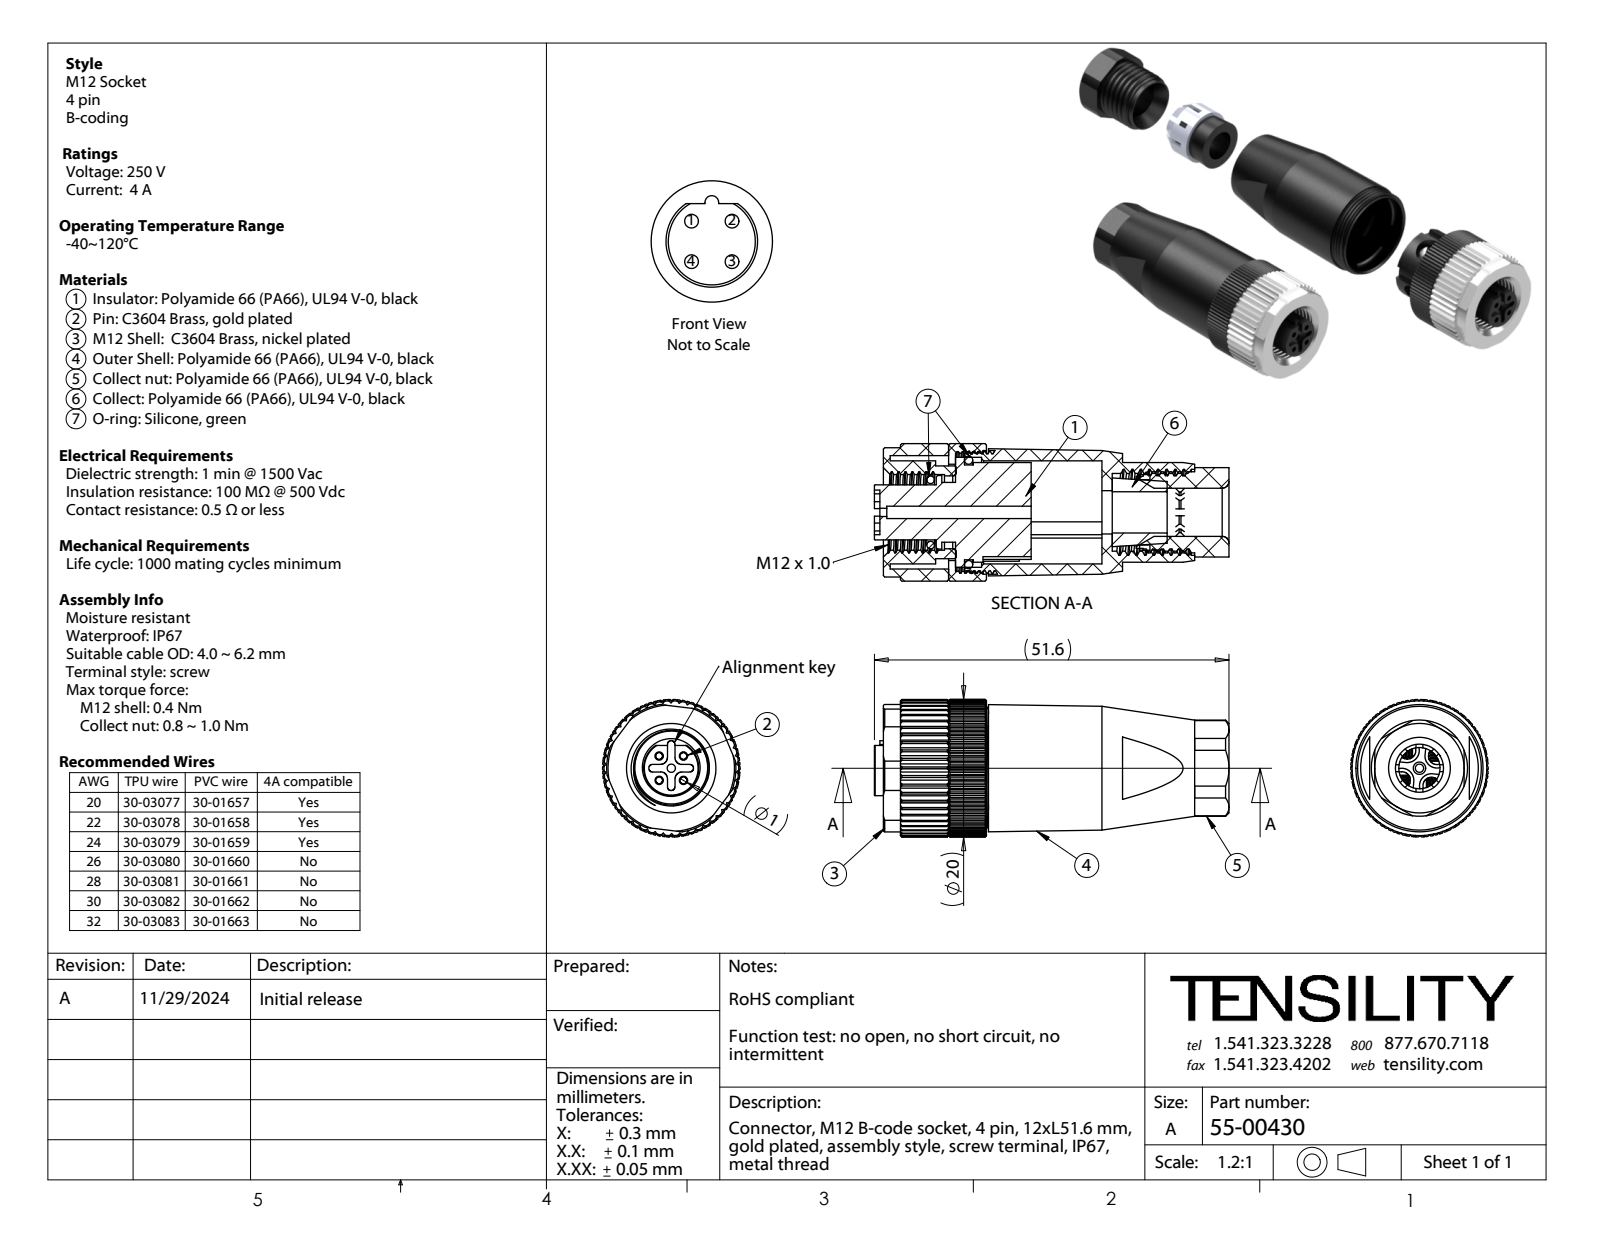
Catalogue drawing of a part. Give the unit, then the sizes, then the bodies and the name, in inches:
Units: inches
Overall size (bounding box): 2.031 × 0.787 × 0.787
Round holes (diameter × count): ⌀0.098 ×8, ⌀0.047 ×5, ⌀0.071 ×5, ⌀0.039 ×4, ⌀0.081 ×4, ⌀0.197 ×4, ⌀0.236 ×1, ⌀0.248 ×1, ⌀0.276 ×1, ⌀0.374 ×1, ⌀0.417 ×1, ⌀0.433 ×1
Round bosses / shafts (diameter × count): ⌀0.138 ×4, ⌀0.094 ×4, ⌀0.701 ×1, ⌀0.67 ×1, ⌀0.669 ×1, ⌀0.571 ×1, ⌀0.551 ×1, ⌀0.543 ×1
Partial cylindrical surfaces — rounded edges, fillets, slot ends (radius × count): R0.022 ×4, R0.039 ×4, R0.069 ×4, R0.209 ×1, R0.254 ×1, R0.256 ×1, R0.37 ×1, R0.394 ×1
Main face-to-face distances: 0.039, 0.374, 0.465, 0.937, 0.878, 0.529, 0.472, 1.252, 0.846, 0.413
Hole centre spacings: 0.202, 0.202, 0.031, 0.098, 0.123, 0.139, 0.143, 0.171
Volume: 0.508 in³ · Surface area: 21.01 in²
Bodies: 16 solids, 1456 faces (525 planar, 499 cylindrical, 432 other)
Part name (STEP PRODUCT): 55-00430-05; 55-00430-03; 55-00430-01; 55-00430-04 (+7 more)
STEP written by: SolidWorks 2021 (CONFIG_CONTROL_DESIGN)
